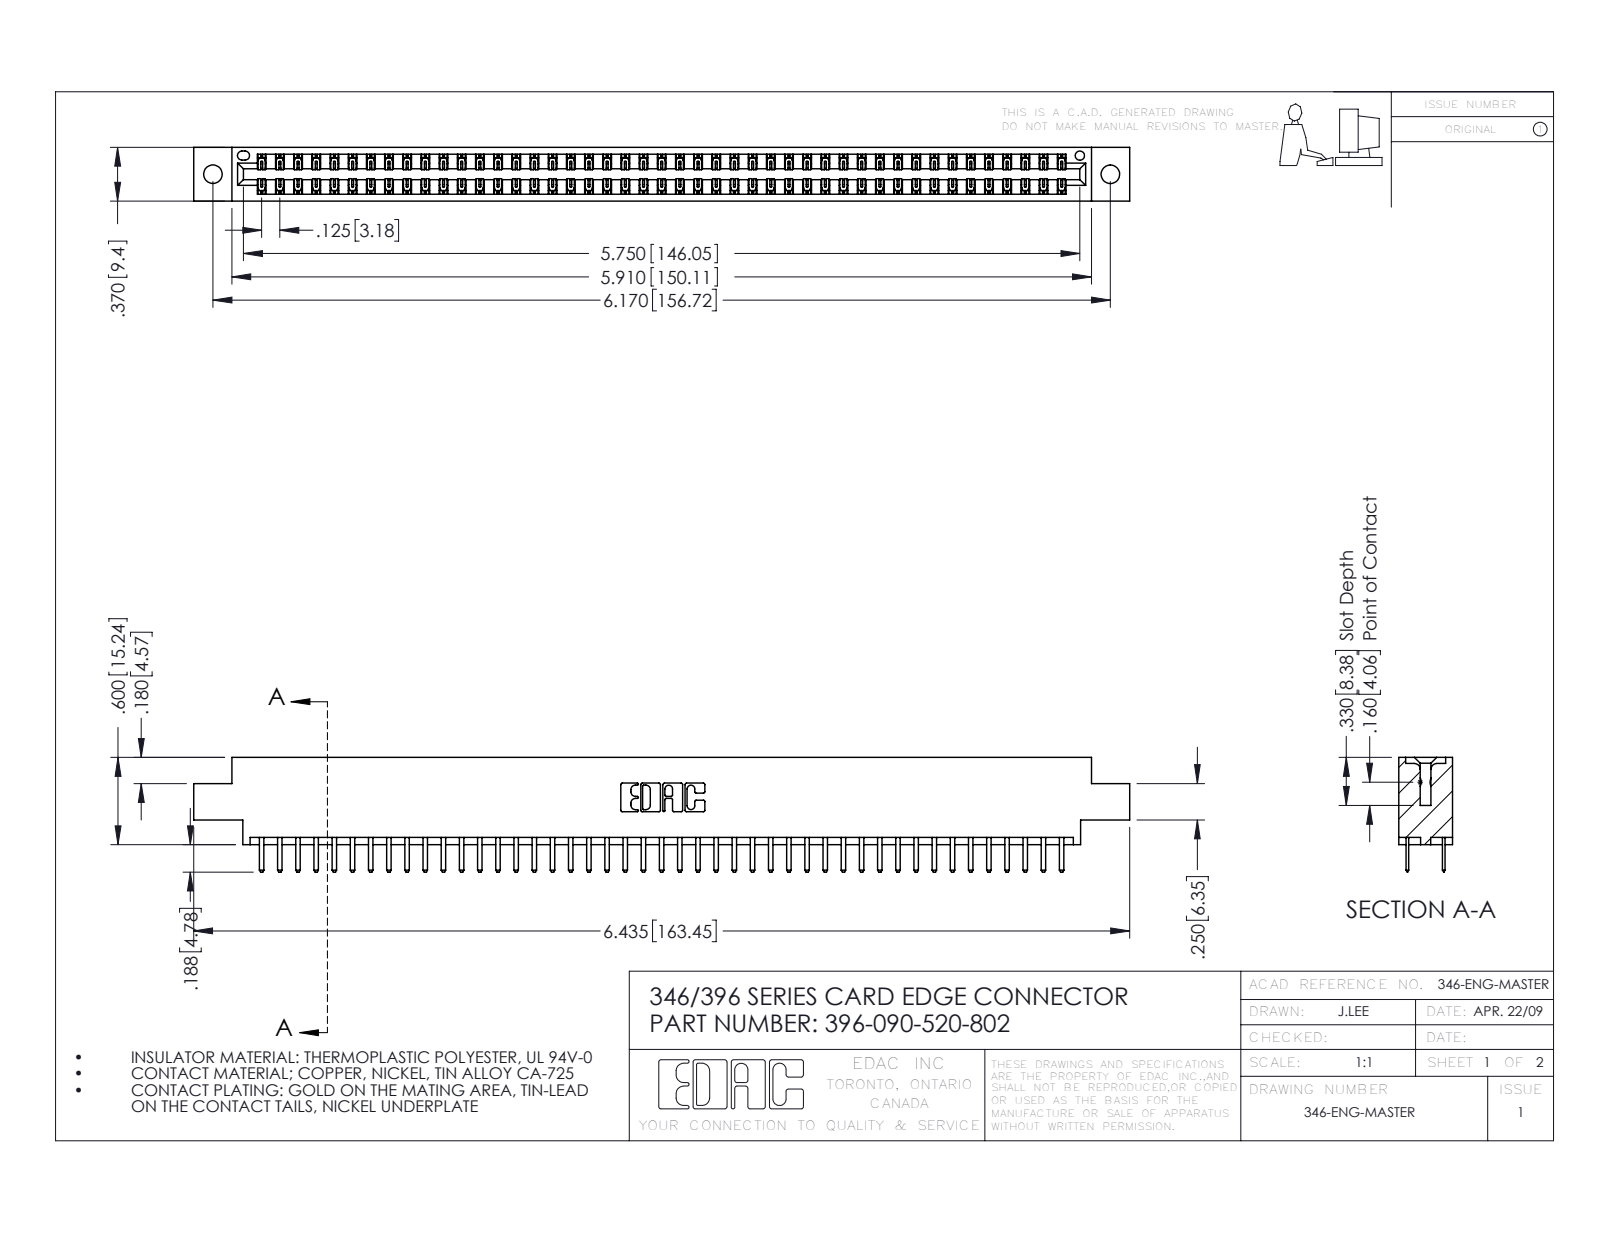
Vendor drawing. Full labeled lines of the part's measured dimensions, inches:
Part name (STEP PRODUCT): 345-292-001_345-293-120; 396-090-520-802; 346 Part_0.170 Offset - 0.128 Dia
STEP written by: SolidWorks 2016 (CONFIG_CONTROL_DESIGN)
Units: inches
Bodies: 91 solids, 5166 faces (3410 planar, 1756 cylindrical, 0 other)
Overall size (bounding box): 6.435 × 0.788 × 0.37
Volume: 0.96 in³ · Surface area: 33.31 in²
Round holes (diameter × count): ⌀0.128 ×2, ⌀0.064 ×1
Partial cylindrical surfaces — rounded edges, fillets, slot ends (radius × count): R0.006 ×135, R0.01 ×94, R0.01 ×22, R0.007 ×6, R0.031 ×6, R0.026 ×3, R0.014 ×2, R0.022 ×2
Main face-to-face distances: 0.048, 0.322, 0.25, 0.37, 0.275, 0.072, 0.298, 0.025, 0.148, 0.222
Hole centre spacings: 0.246, 5.961, 6.17
